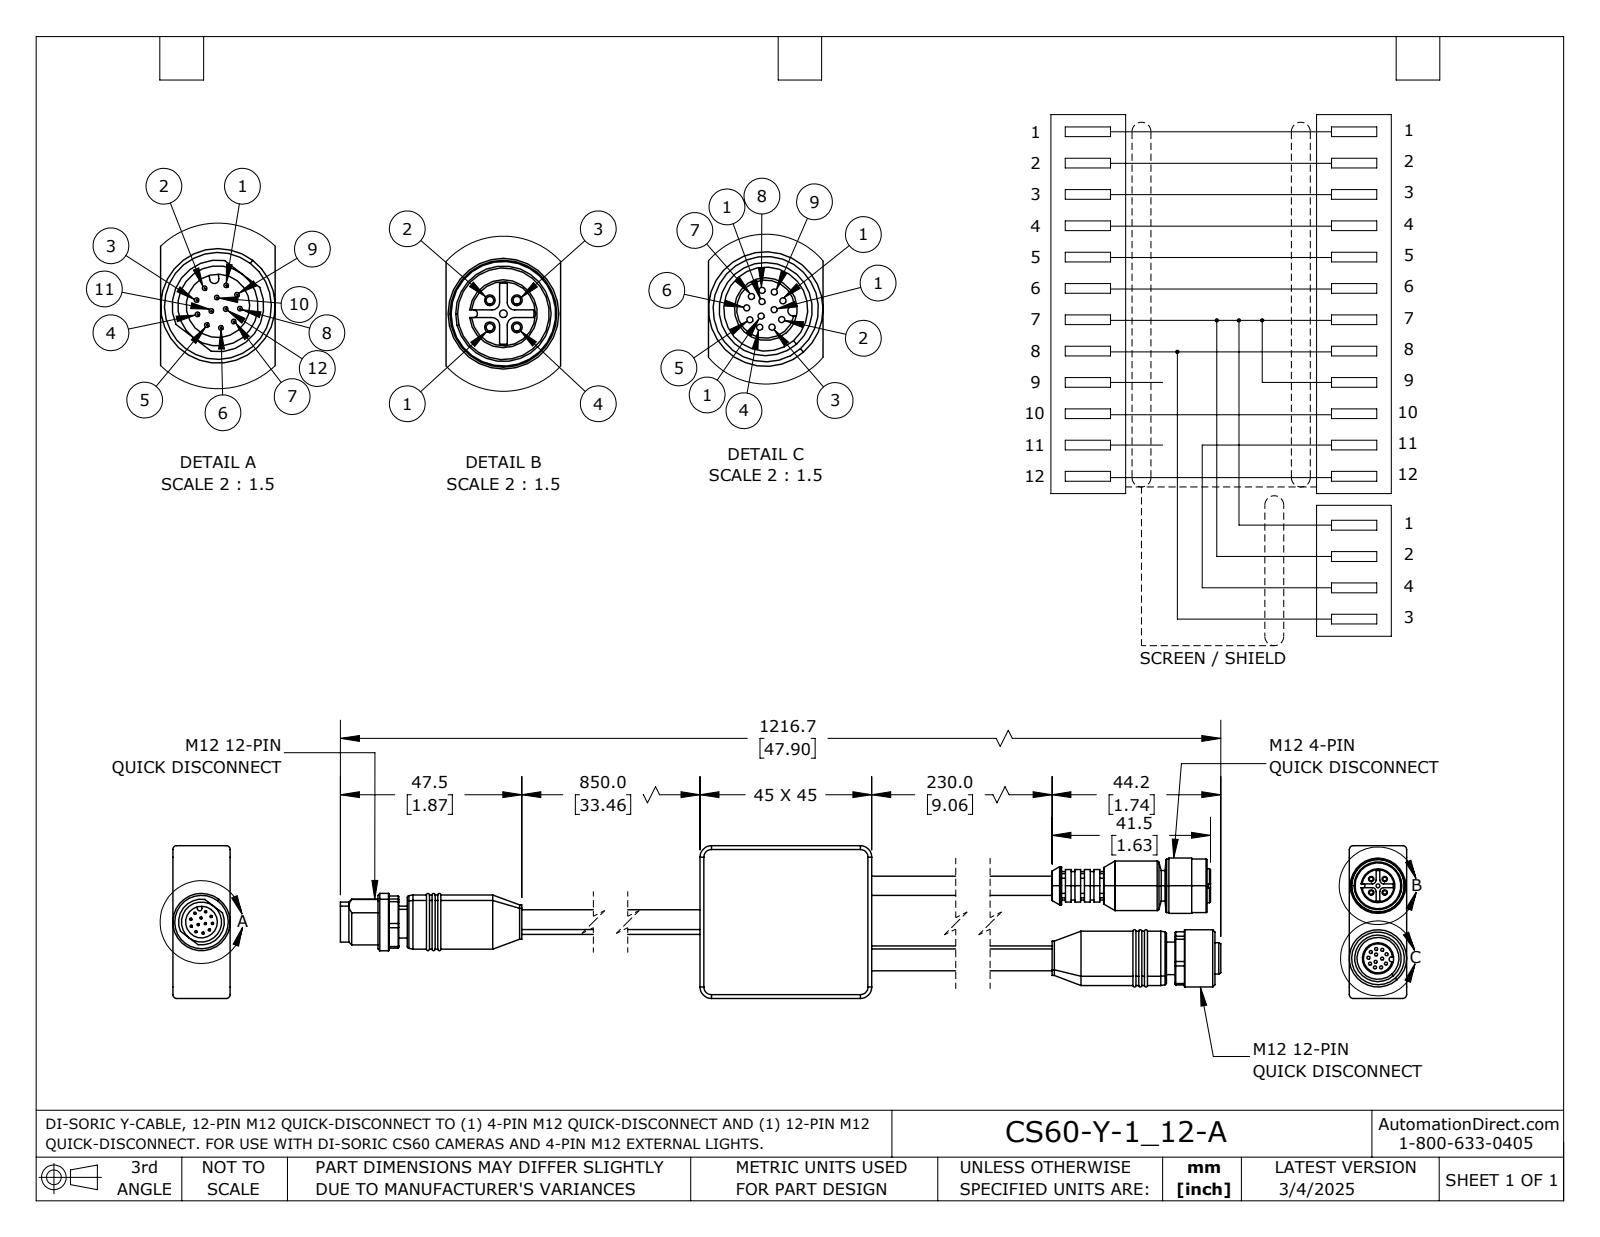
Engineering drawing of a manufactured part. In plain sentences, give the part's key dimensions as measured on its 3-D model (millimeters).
The part is named "CS60-Y-1_12-A". Its 3-D file was written by "SolidWorks 2024 (AUTOMOTIVE_DESIGN)". It is 4 solids with 335 faces: 142 planar, 122 cylindrical and 71 other. Overall it measures 1216.7 by 40 by 15 millimeters. Its volume is 80 960 cubic millimeters and its surface area 45 054 square millimeters. Round holes: 12 of diameter 0.8, 5 of diameter 1, 4 of diameter 1.67, 2 of diameter 5, 2 of diameter 6.5, 1 of diameter 8, 1 of diameter 8.3, 1 of diameter 11, 1 of diameter 12. Round bosses or shafts: 12 of diameter 0.6, 2 of diameter 15, 2 of diameter 14.2, 2 of diameter 9, 2 of diameter 8.5, 1 of diameter 14.5, 1 of diameter 14, 1 of diameter 13. Partial cylindrical surfaces (rounded edges, fillets, slot ends): 12 of radius 1, 4 of radius 3, 2 of radius 7.2, 1 of radius 0.5, 1 of radius 0.6, 1 of radius 0.65, 1 of radius 6. The main face-to-face distances are 15, 40, 45, 2.2, 1187.2, 30, 32.2, 1157.2, 1155, 44.9. The hole center spacings are 2.5, 1.61, 2.81, 3.05, 4.83, 1.22, 1.29, 1.82.
